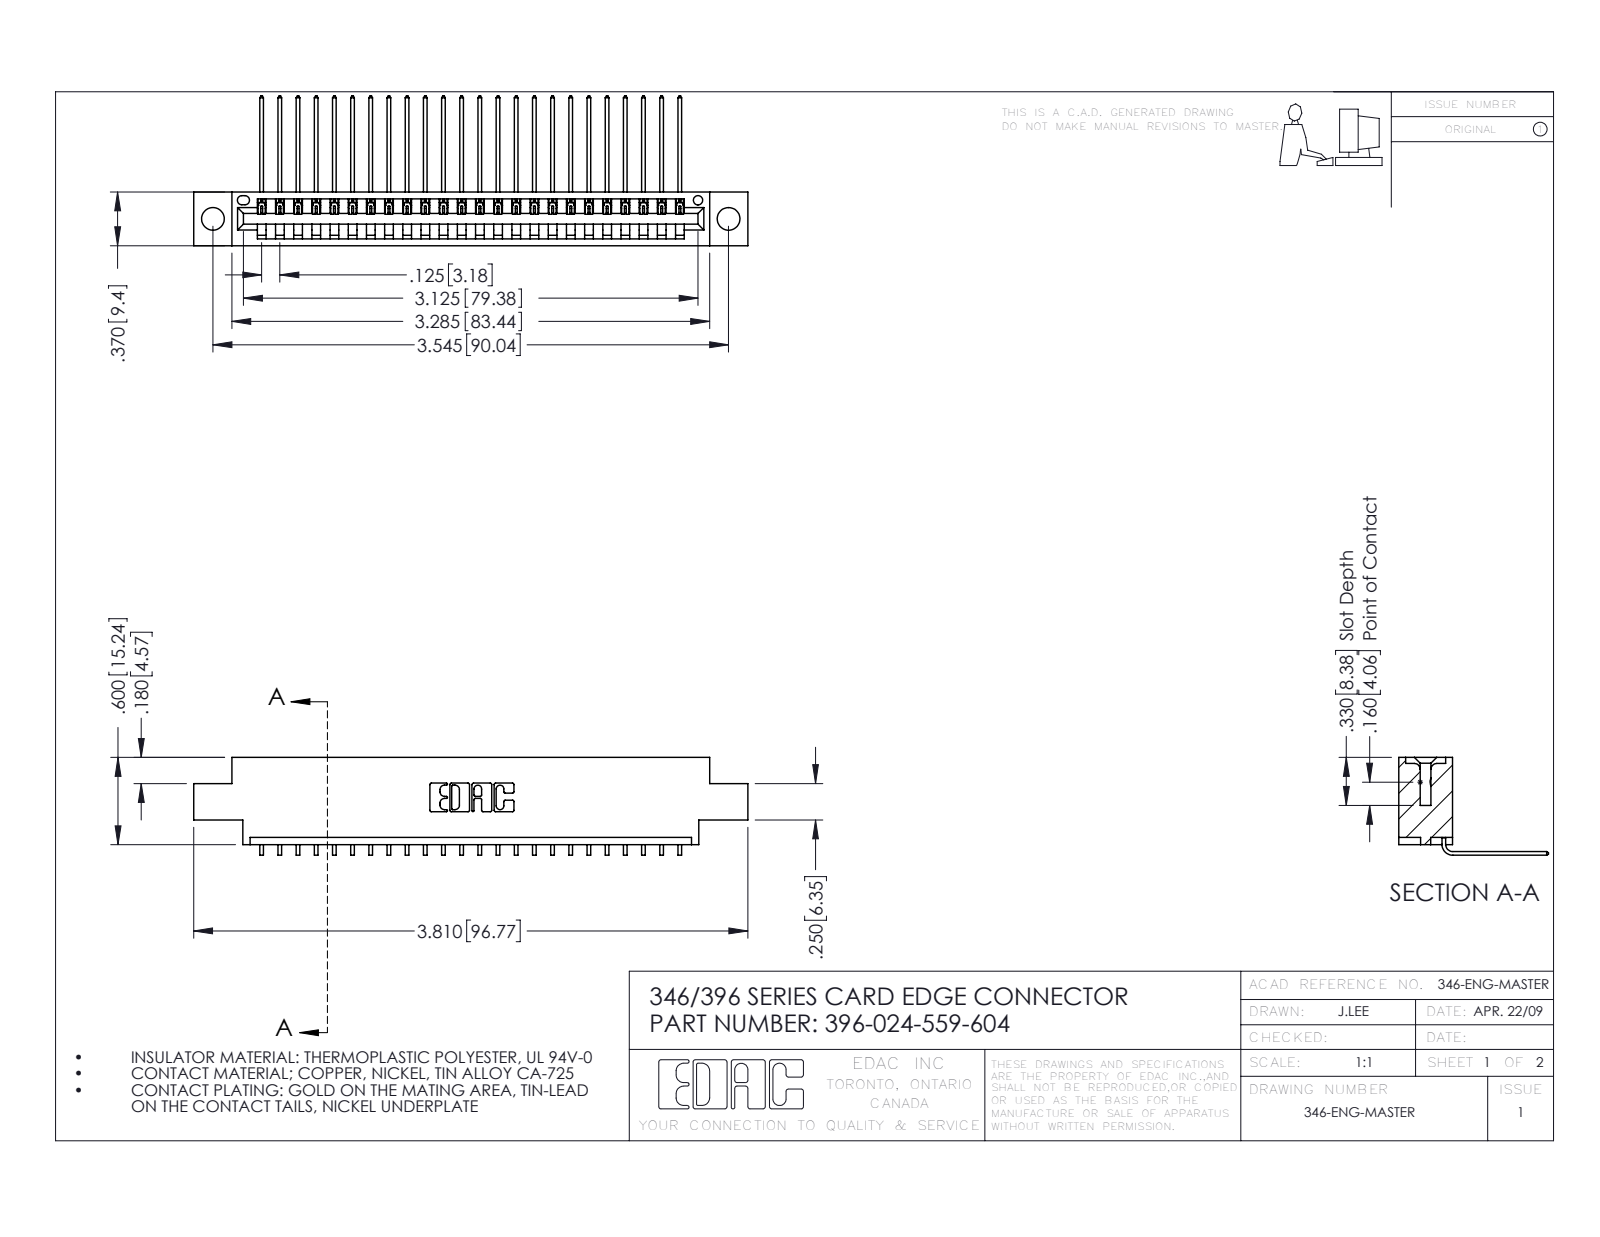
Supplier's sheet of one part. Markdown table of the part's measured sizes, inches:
| quantity | value |
| --- | --- |
| part name | 346 Part_0.170 Offset - 0.156 Dia-TH; 345-292-001_558 559 Tail - 1; 396-024-559-604 |
| STEP written by | SolidWorks 2016 (CONFIG_CONTROL_DESIGN) |
| units | inches |
| bodies | 25 solids, 1566 faces (1088 planar, 478 cylindrical, 0 other) |
| overall size | 3.81 × 1.03 × 0.673 |
| volume | 0.548 in³ |
| surface area | 17.78 in² |
| round holes (diameter × count) | 0.156 × 2, 0.064 × 1 |
| partial cylindrical surfaces (radius × count) | 0.006 × 48, 0.01 × 22, 0.007 × 6, 0.031 × 6, 0.026 × 3, 0.031 × 2, 0.04 × 2, 0.014 × 1 |
| main face-to-face distances | 0.048, 0.322, 0.37, 0.25, 0.025, 0.072, 0.148, 0.222, 0.1, 0.174 |
| hole center spacings | 0.246, 3.337, 3.545 |
